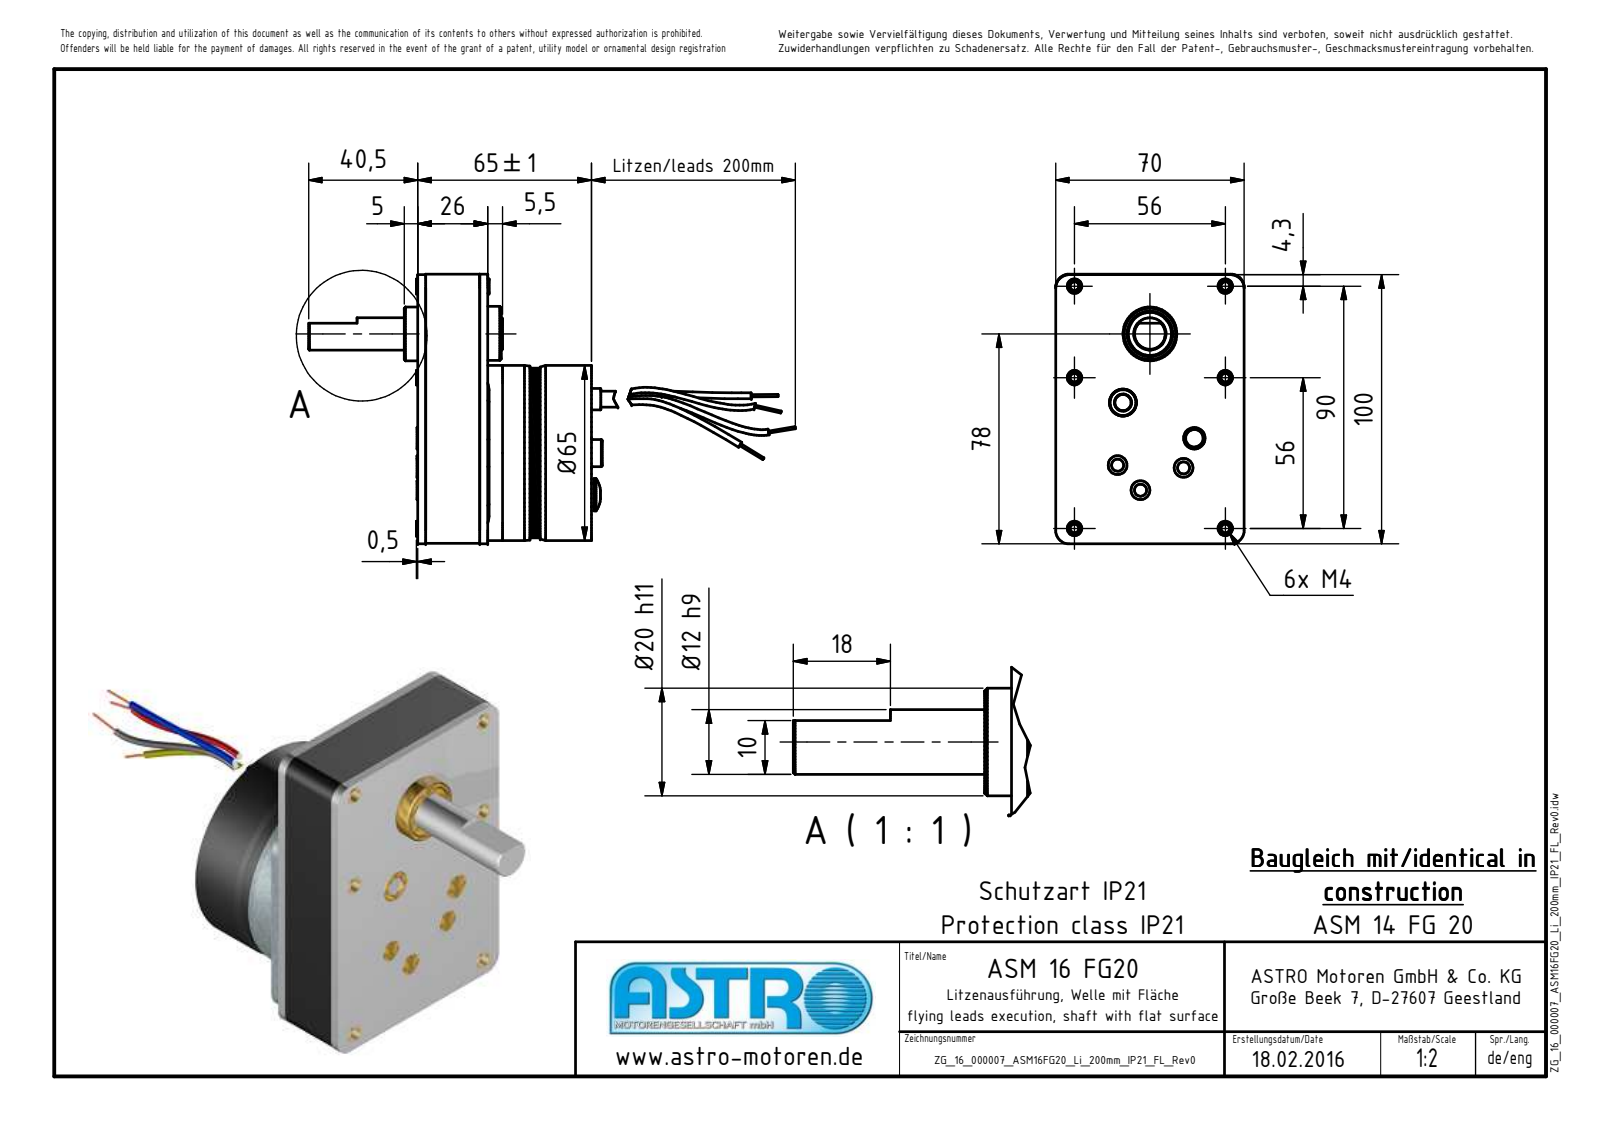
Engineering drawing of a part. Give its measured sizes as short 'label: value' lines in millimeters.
name: ZG_16_000007_ASM16FG20_Li_200mm_IP21_FL_Rev0; AFG-20_Welle_FL_18; FG-Antriebsseite20; FG-Abstandhalter (+8 more)
written by: Autodesk Inventor 2010 (AUTOMOTIVE_DESIGN)
unit: mm
bodies: 20 solids, 493 faces (181 planar, 148 cylindrical, 164 other)
size: 180.73 × 100.2 × 70
volume: 143 556 mm³; area: 97 286 mm²
holes: 8× ⌀4.1, 7× ⌀5, 3× ⌀4.5, 3× ⌀10, 3× ⌀16, 2× ⌀6, 1× ⌀5.5, 1× ⌀6.5, 1× ⌀12, 1× ⌀14, 1× ⌀15.5, 1× ⌀59
bosses: 8× ⌀8, 6× ⌀5.39, 6× ⌀4.84, 3× ⌀7, 3× ⌀0.8, 2× ⌀20, 2× ⌀12.01, 2× ⌀8.5
rounds: 8× R0.5, 8× R1, 8× R2.25, 8× R5, 4× R3.15, 4× R5.26, 4× R6.5
face distances: 3, 23, 20, 26, 16, 25.5, 26.5, 3.5, 1.85, 9.5
hole spacings: 27, 28.02, 61.72, 20.66, 38.18, 49.89, 56, 39.6
